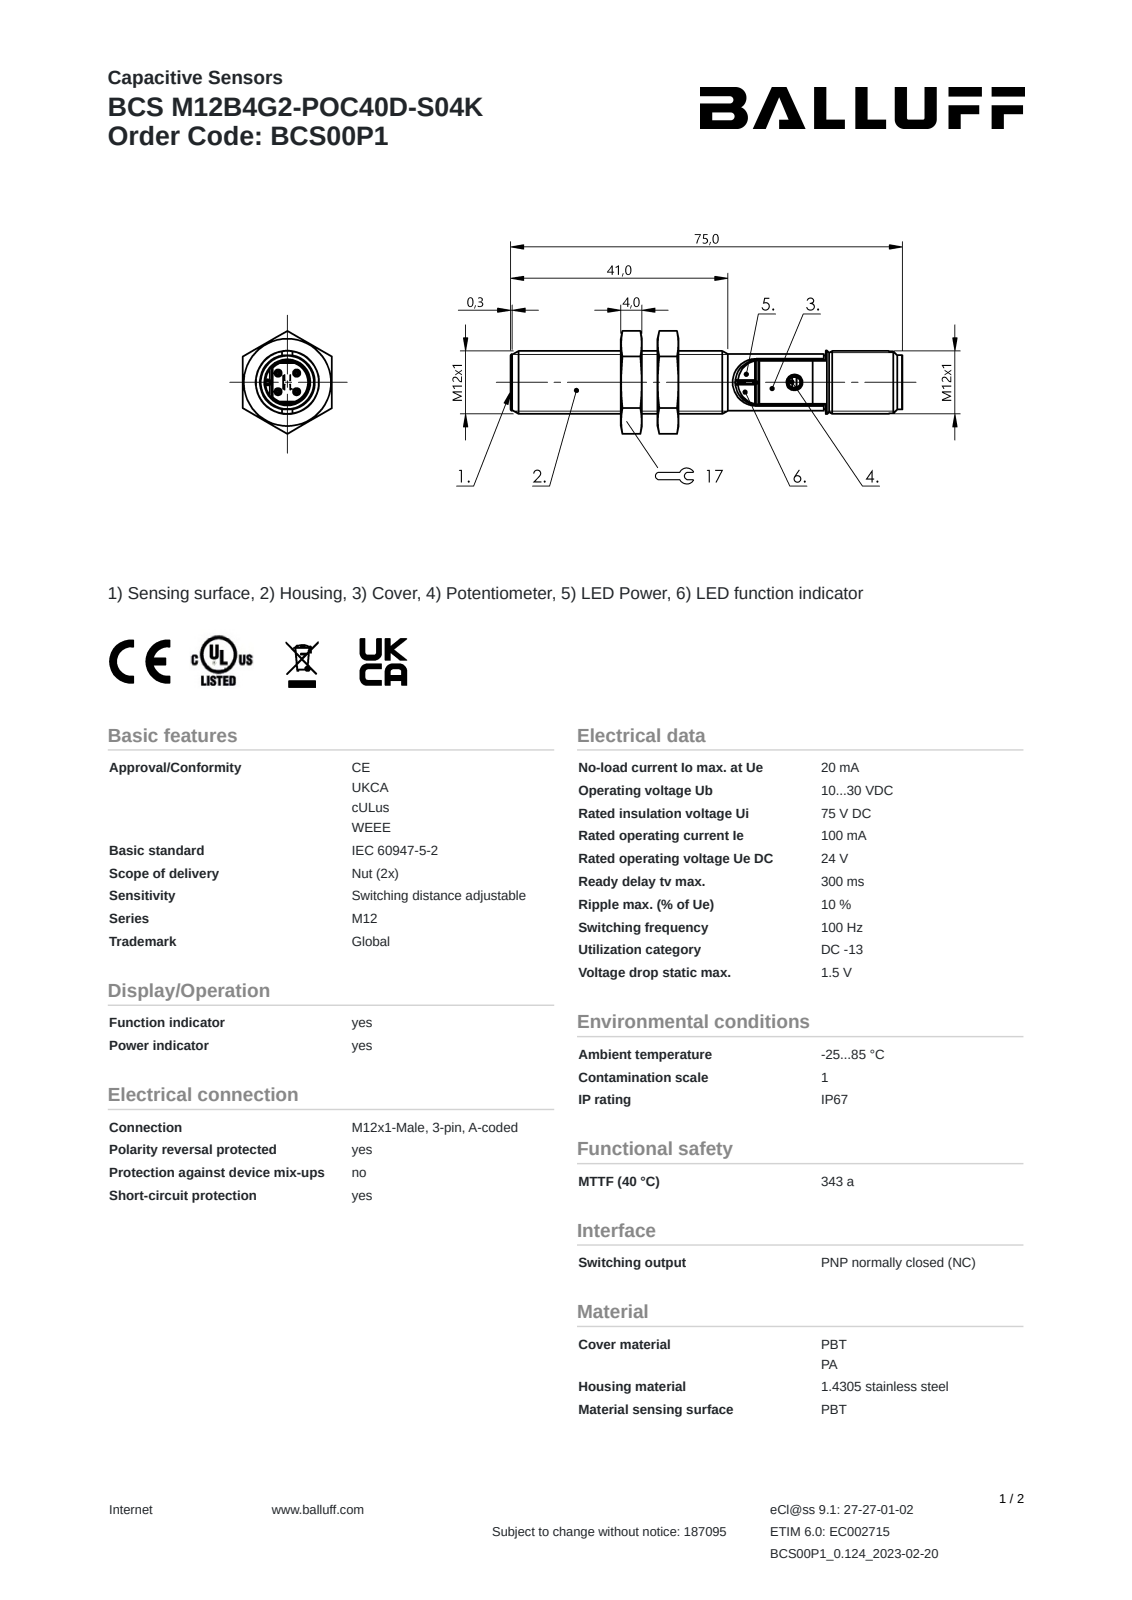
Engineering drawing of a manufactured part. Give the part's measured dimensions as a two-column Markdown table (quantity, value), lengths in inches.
| quantity | value |
| --- | --- |
| part name | BCS00P1 |
| STEP written by | SolidWorks 2021 (AUTOMOTIVE_DESIGN) |
| units | inches |
| bodies | 3 solids, 179 faces (86 planar, 49 cylindrical, 44 other) |
| overall size | 2.953 × 0.773 × 0.669 |
| volume | 0.53 in³ |
| surface area | 7.467 in² |
| round holes (diameter × count) | 0.135 × 1, 0.331 × 1, 0.43 × 1 |
| round bosses / shafts (diameter × count) | 0.039 × 4, 0.472 × 1, 0.467 × 1, 0.423 × 1, 0.407 × 1, 0.406 × 1 |
| partial cylindrical surfaces (radius × count) | 0.004 × 8, 0.006 × 2, 0.009 × 2, 0.01 × 1, 0.024 × 1, 0.061 × 1, 0.156 × 1, 0.157 × 1 |
| main face-to-face distances | 0.276, 0.157, 0.669, 0.433, 0.118, 0.413, 0.846, 0.689, 0.571, 1.76 |
